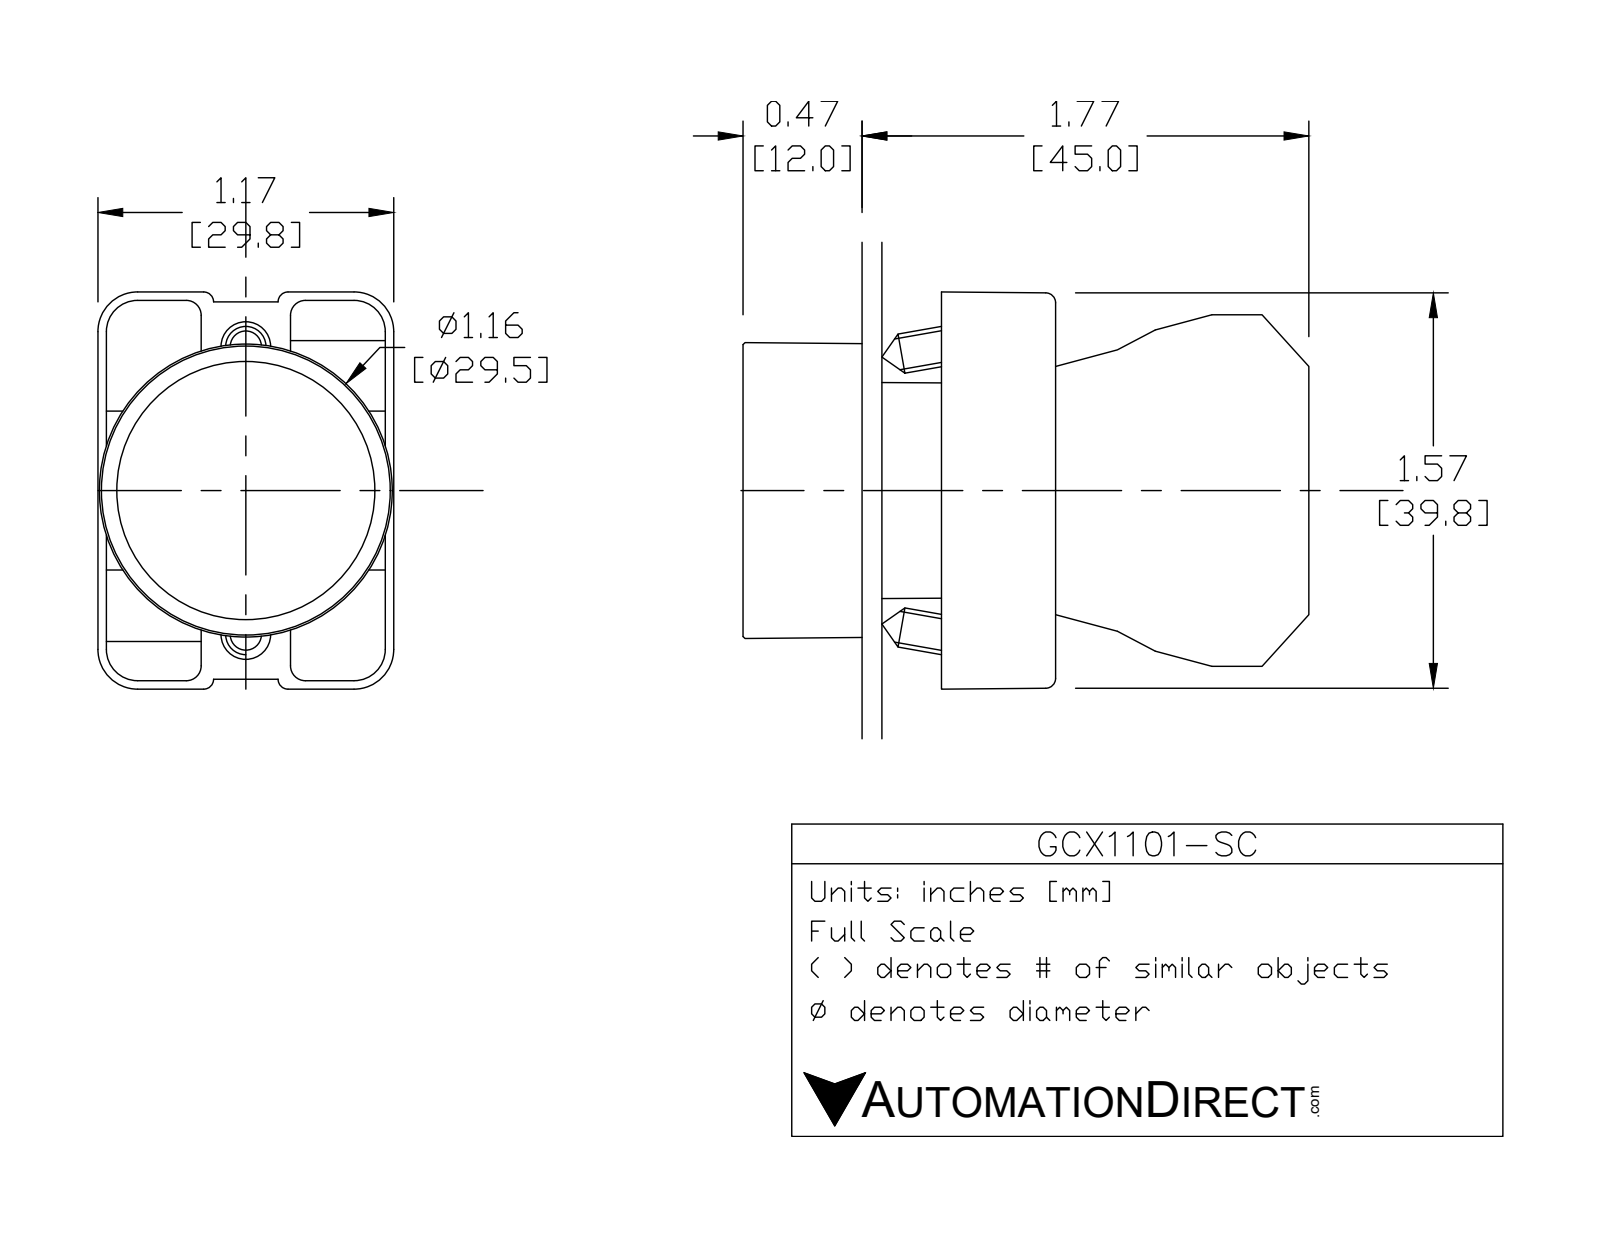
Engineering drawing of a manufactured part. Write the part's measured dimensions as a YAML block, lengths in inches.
part_name: "ecx1029; GCX1101 OPERATOR; GCX1101-SC"
step_written_by: "SolidWorks 2016 (AUTOMOTIVE_DESIGN)"
units: inches
bodies: {solids: 5, faces: 288, planar: 147, cylindrical: 118, other: 23}
overall_size: [1.581, 1.407, 1.177]
volume: 1.09
surface_area: 20.41
round_holes:
  - {diameter: 0.124, count: 2}
  - {diameter: 0.13, count: 2}
  - {diameter: 0.197, count: 1}
  - {diameter: 0.878, count: 1}
  - {diameter: 0.888, count: 1}
  - {diameter: 1.024, count: 1}
round_bosses_or_shafts:
  - {diameter: 0.157, count: 2}
  - {diameter: 1.175, count: 1}
  - {diameter: 1.004, count: 1}
  - {diameter: 0.945, count: 1}
  - {diameter: 0.856, count: 1}
  - {diameter: 0.78, count: 1}
partial_cylinders:
  - {radius: 0.059, count: 24}
  - {radius: 0.041, count: 12}
  - {radius: 0.124, count: 12}
  - {radius: 0.157, count: 12}
  - {radius: 0.039, count: 4}
  - {radius: 0.128, count: 2}
  - {radius: 0.392, count: 1}
  - {radius: 0.398, count: 1}
face_to_face_distances: [0.033, 0.72, 1.193, 0.472, 0.031, 0.689, 1.161, 0.122, 0.091, 0.598]
